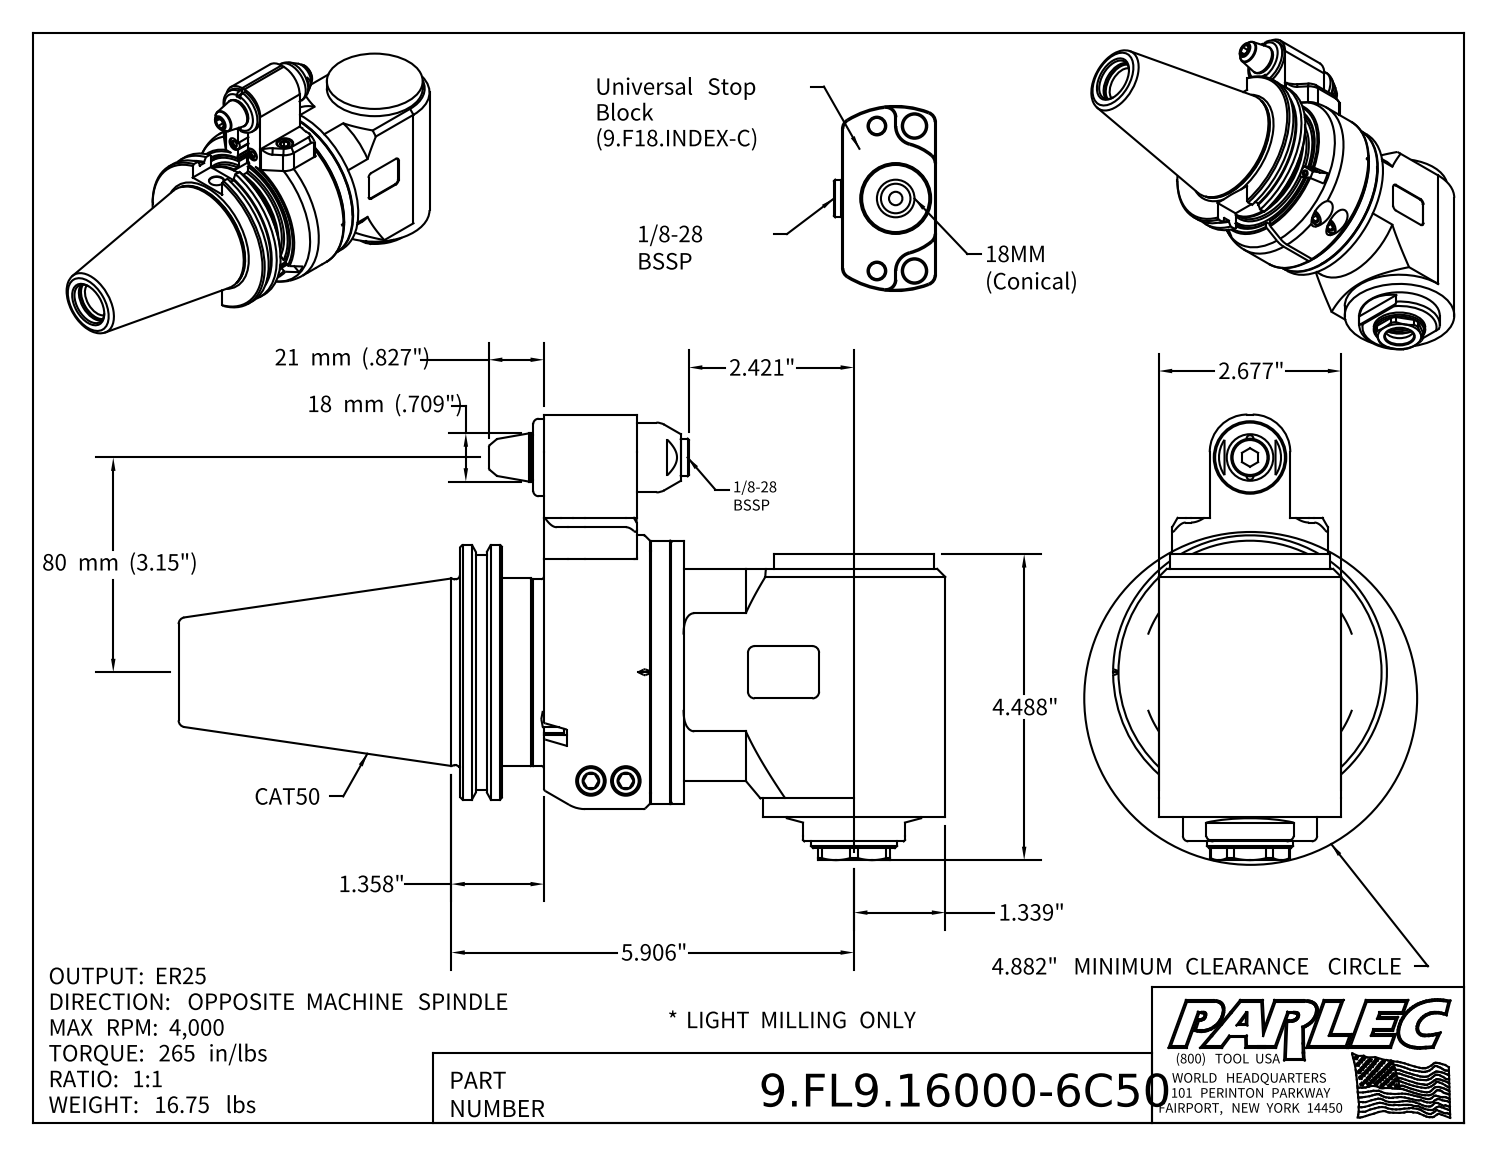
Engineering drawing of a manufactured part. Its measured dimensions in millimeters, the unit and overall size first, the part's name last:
Units: millimetres
Overall size (bounding box): 285.6 × 166 × 102
Round holes (diameter × count): ⌀5 ×3, ⌀8 ×3, ⌀2.6 ×2, ⌀3.3 ×2, ⌀4.2 ×2, ⌀6.5 ×2, ⌀10.4 ×2, ⌀11 ×2, ⌀12.5 ×2, ⌀2.5 ×1, ⌀3 ×1, ⌀6 ×1
Round bosses / shafts (diameter × count): ⌀10 ×5, ⌀18 ×2, ⌀12 ×2, ⌀6 ×2, ⌀102 ×1, ⌀98.4 ×1, ⌀98 ×1, ⌀91.3 ×1
Partial cylindrical surfaces — rounded edges, fillets, slot ends (radius × count): R1 ×14, R3 ×6, R2.5 ×4, R4 ×4, R0.5 ×2, R8 ×2, R14 ×2, R14.8 ×1
Main face-to-face distances: 32, 68, 54.9, 23, 12.5, 44.5, 70.8, 38.8, 15.9, 19
Hole centre spacings: 7, 24.4, 31, 37.8, 50.6, 1.2, 13, 14
Volume: 1 270 000 mm³ · Surface area: 159 200 mm²
Bodies: 4 solids, 531 faces (258 planar, 143 cylindrical, 130 other)
Part name (STEP PRODUCT): 9.FL9.16000-4C50; 9_FL9_16000; 9GA15C_458 (EVO, Type 1, Cat50, 80mm, Conical)
STEP written by: Autodesk Inventor 2022 (AUTOMOTIVE_DESIGN)
